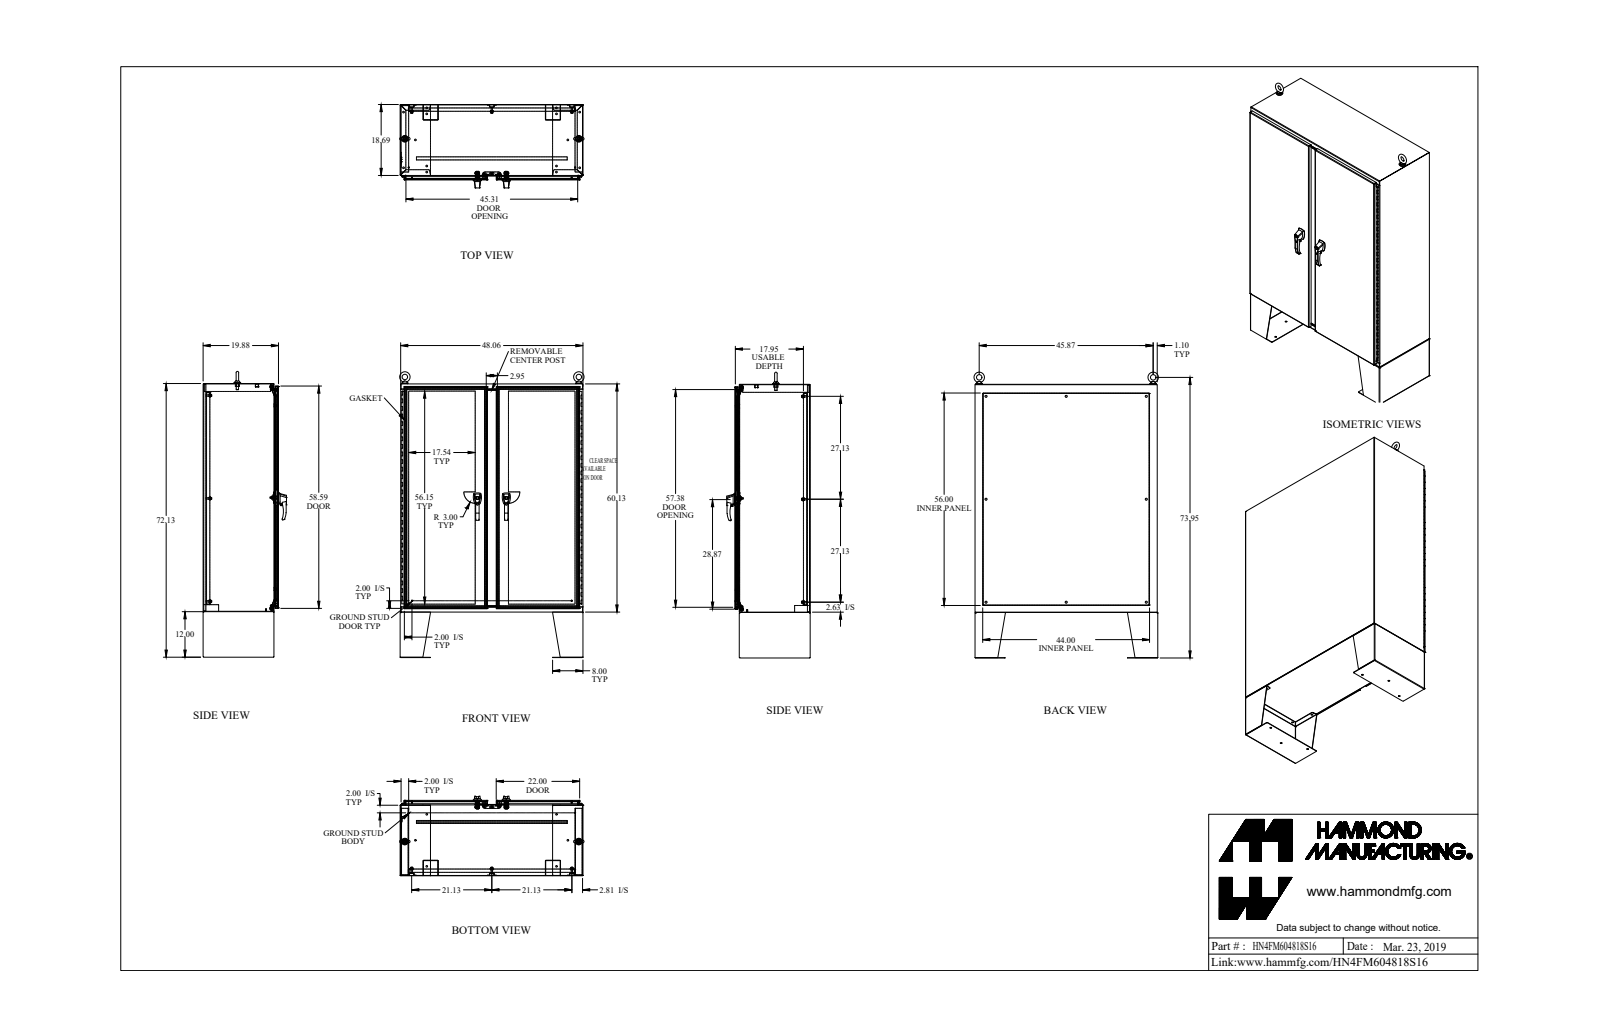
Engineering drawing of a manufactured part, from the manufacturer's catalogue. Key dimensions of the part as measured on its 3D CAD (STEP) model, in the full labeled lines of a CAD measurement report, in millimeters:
Part name (STEP PRODUCT): HN4FM604818S16
STEP written by: SolidWorks 2018 (AUTOMOTIVE_DESIGN)
Units: millimetres
Bodies: 134 solids, 3784 faces (1748 planar, 1675 cylindrical, 361 other)
Overall size (bounding box): 1913.2 × 1234.6 × 558.5
Volume: 26 690 000 mm³ · Surface area: 21 320 000 mm²
Round holes (diameter × count): ⌀7.7 ×20, ⌀11.1 ×14, ⌀7.8 ×8, ⌀8.9 ×8, ⌀14.3 ×8, ⌀6.4 ×6, ⌀11.3 ×6, ⌀7.1 ×4, ⌀8 ×4, ⌀9.9 ×4, ⌀5.1 ×3, ⌀8 ×3
Round bosses / shafts (diameter × count): ⌀25.4 ×10, ⌀16.5 ×8, ⌀9.5 ×8, ⌀8.4 ×8, ⌀19.1 ×4, ⌀15.9 ×4, ⌀11.2 ×4, ⌀9.4 ×4
Partial cylindrical surfaces — rounded edges, fillets, slot ends (radius × count): R12.7 ×33, R0.5 ×32, R3.2 ×32, R1.2 ×29, R3.6 ×29, R1.5 ×28, R0.8 ×12, R2.3 ×12
Main face-to-face distances: 2.4, 502.4, 500, 3.2, 504.8, 457.1, 45.3, 42.8, 459.6, 42.1
Hole centre spacings: 152.4, 304.8, 457.2, 609.6, 762, 1182.9, 40.9, 156.1
